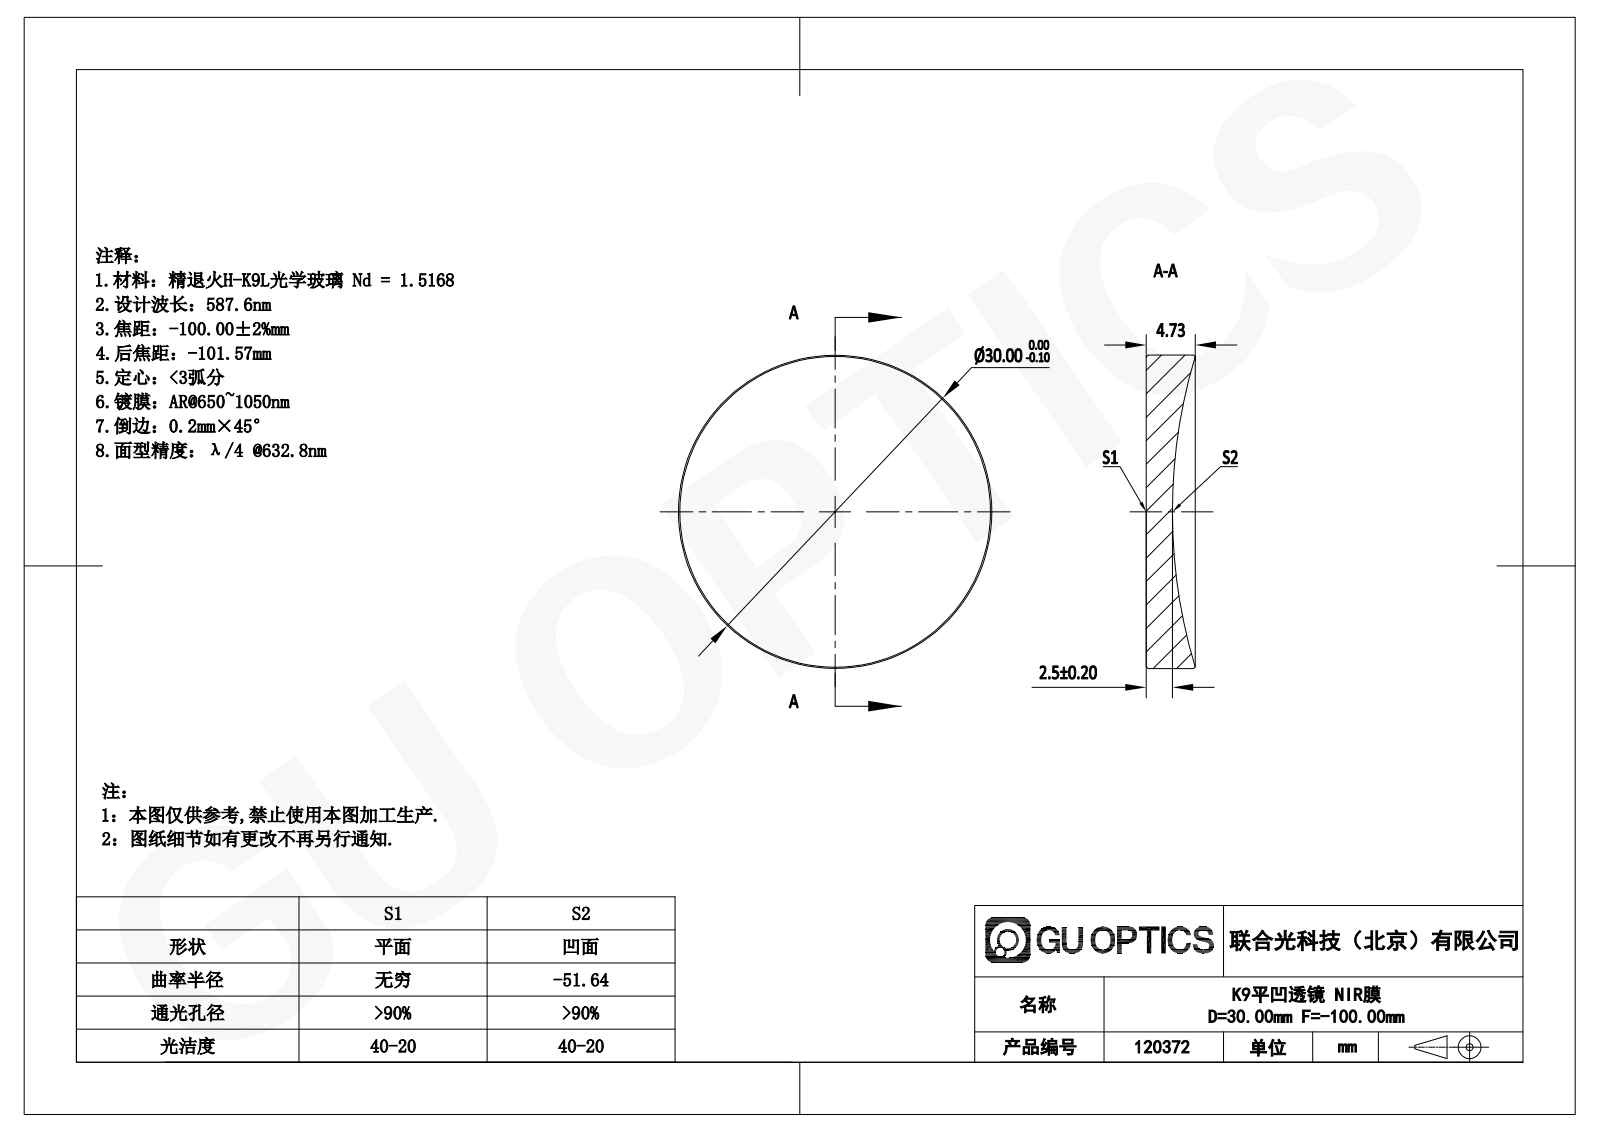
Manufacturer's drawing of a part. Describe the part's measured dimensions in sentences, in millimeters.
The part is named "GL13-030-100". Its 3-D file was written by "SolidWorks 2022 (AUTOMOTIVE_DESIGN)". It is 1 solid with 9 faces: 1 planar, 2 cylindrical and 6 other. Overall it measures 30 by 30 by 4.68 millimeters. Its volume is 2 547 cubic millimeters and its surface area 1 850 square millimeters. Round bosses or shafts: 1 of diameter 30.
